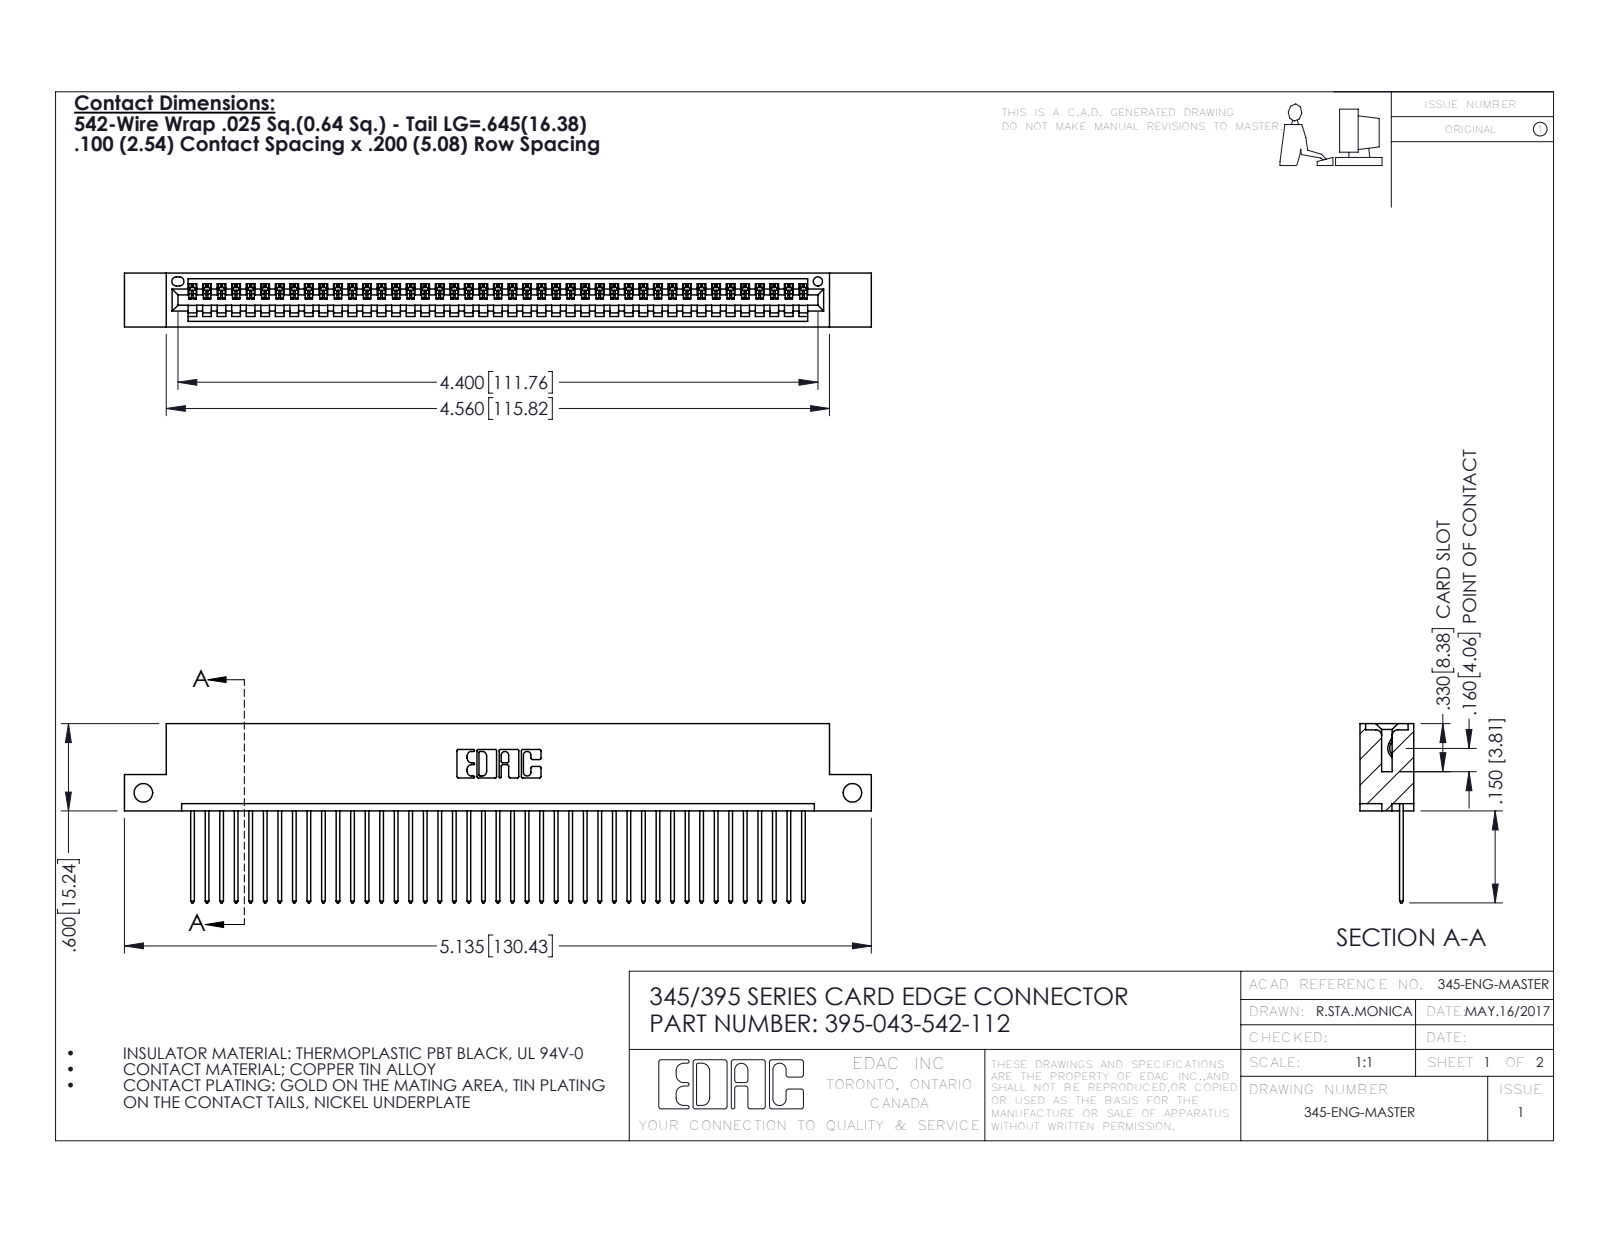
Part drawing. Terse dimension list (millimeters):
name: 345-292-001_345-293-142; 345 Part_Flush Mounting Lugs - Side Mount; 395-043-542-112
written by: SolidWorks 2016 (CONFIG_CONTROL_DESIGN)
unit: mm
bodies: 44 solids, 2620 faces (1800 planar, 820 cylindrical, 0 other)
size: 130.4 × 31.3 × 9.4
volume: 12 400 mm³; area: 16 960 mm²
holes: 2× ⌀3.3, 1× ⌀1.6
rounds: 86× R0.2, 86× R0.3, 22× R0.3, 6× R0.2, 6× R0.8, 3× R0.7, 2× R0.8, 2× R1
face distances: 1.8, 7.6, 9.4, 2.5, 6.9, 0.6, 5.1, 5.7, 3.8, 1.8
hole spacings: 123.8
